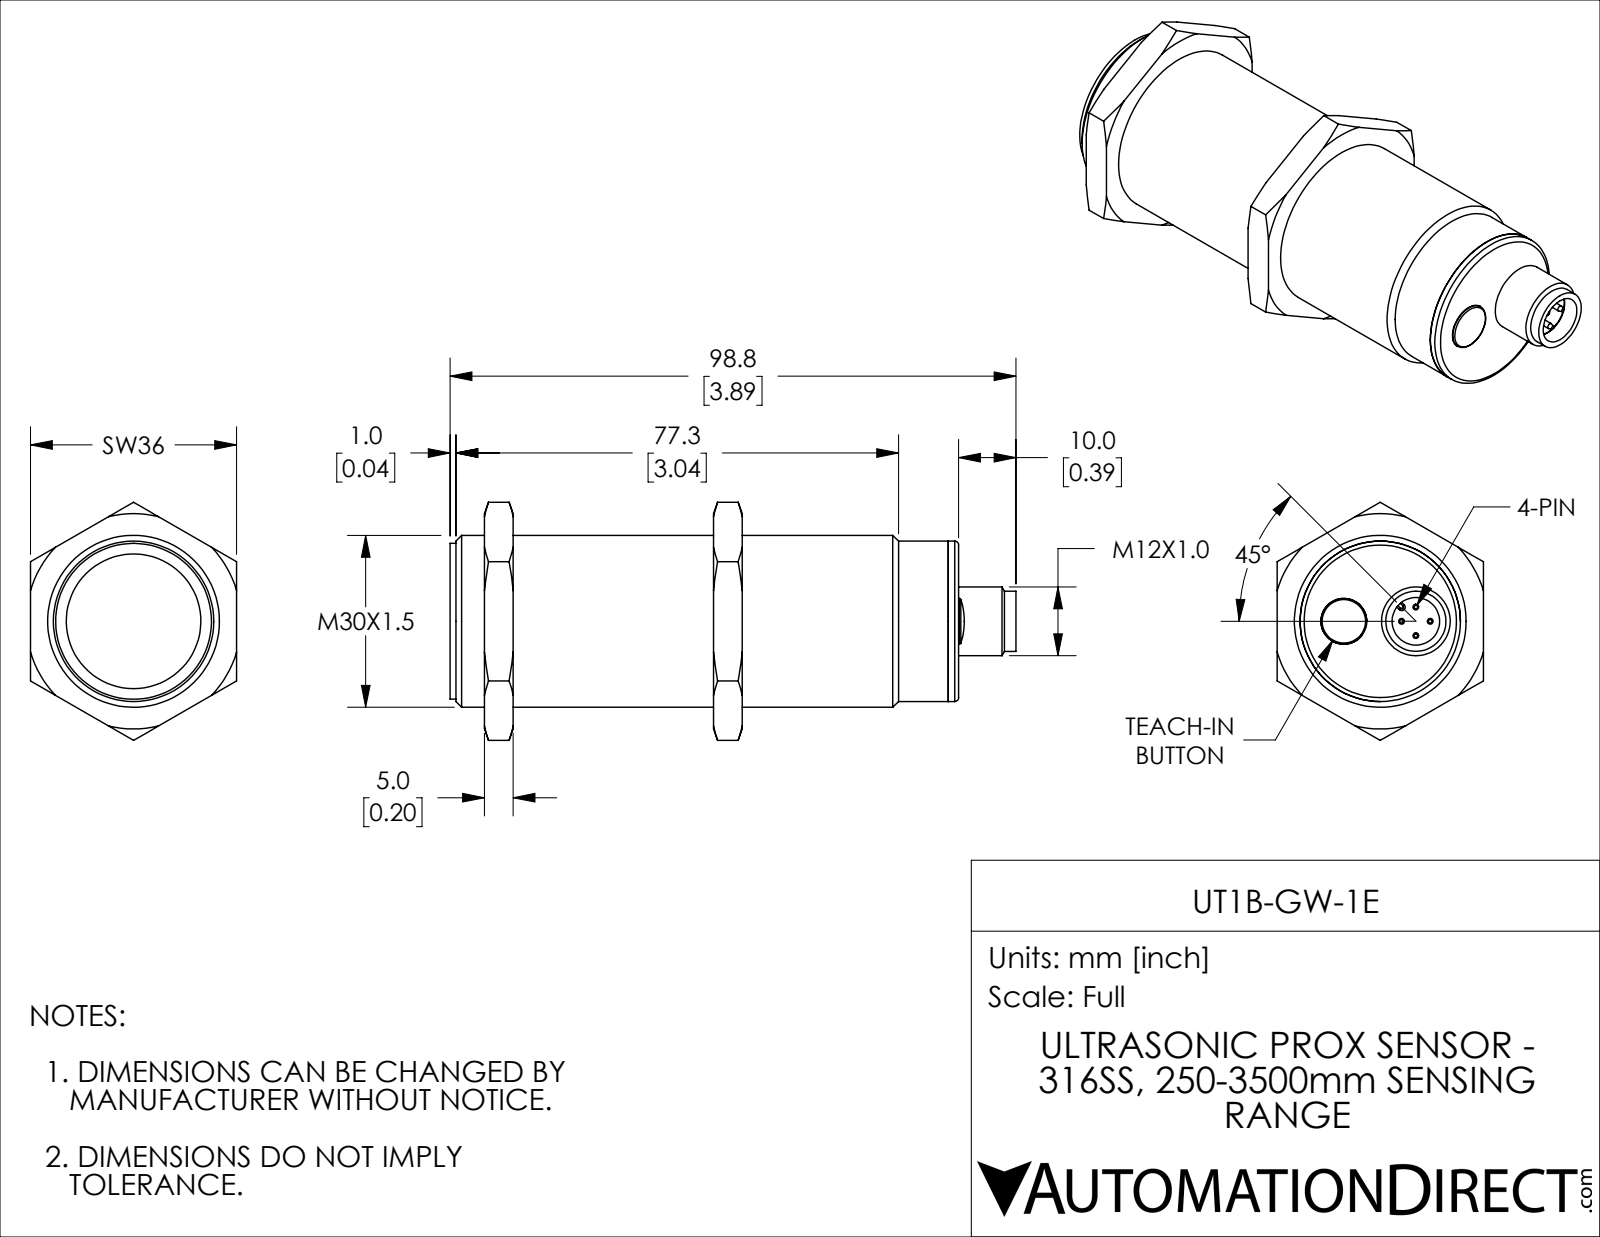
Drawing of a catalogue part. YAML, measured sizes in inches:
part_name: "UT1B-GW-1E"
step_written_by: "SolidWorks 2018 (AUTOMOTIVE_DESIGN)"
units: inches
bodies: {solids: 7, faces: 152, planar: 46, cylindrical: 49, other: 57}
overall_size: [3.89, 1.637, 1.417]
volume: 4.048
surface_area: 26.65
round_holes:
  - {diameter: 0.071, count: 4}
  - {diameter: 0.315, count: 1}
  - {diameter: 0.327, count: 1}
  - {diameter: 0.372, count: 1}
  - {diameter: 0.925, count: 1}
  - {diameter: 1.181, count: 1}
round_bosses_or_shafts:
  - {diameter: 0.039, count: 4}
  - {diameter: 1.102, count: 1}
  - {diameter: 1.071, count: 1}
  - {diameter: 0.472, count: 1}
  - {diameter: 0.413, count: 1}
  - {diameter: 0.364, count: 1}
partial_cylinders:
  - {radius: 0.012, count: 2}
  - {radius: 0.024, count: 1}
face_to_face_distances: [3.386, 0.197, 1.417, 1.772, 1.575, 3.457, 0.039, 3.425, 0.394, 0.071]
hole_center_spacings: [0.098, 0.139, 0.197, 0.264, 0.505, 0.146, 0.245, 0.25]
